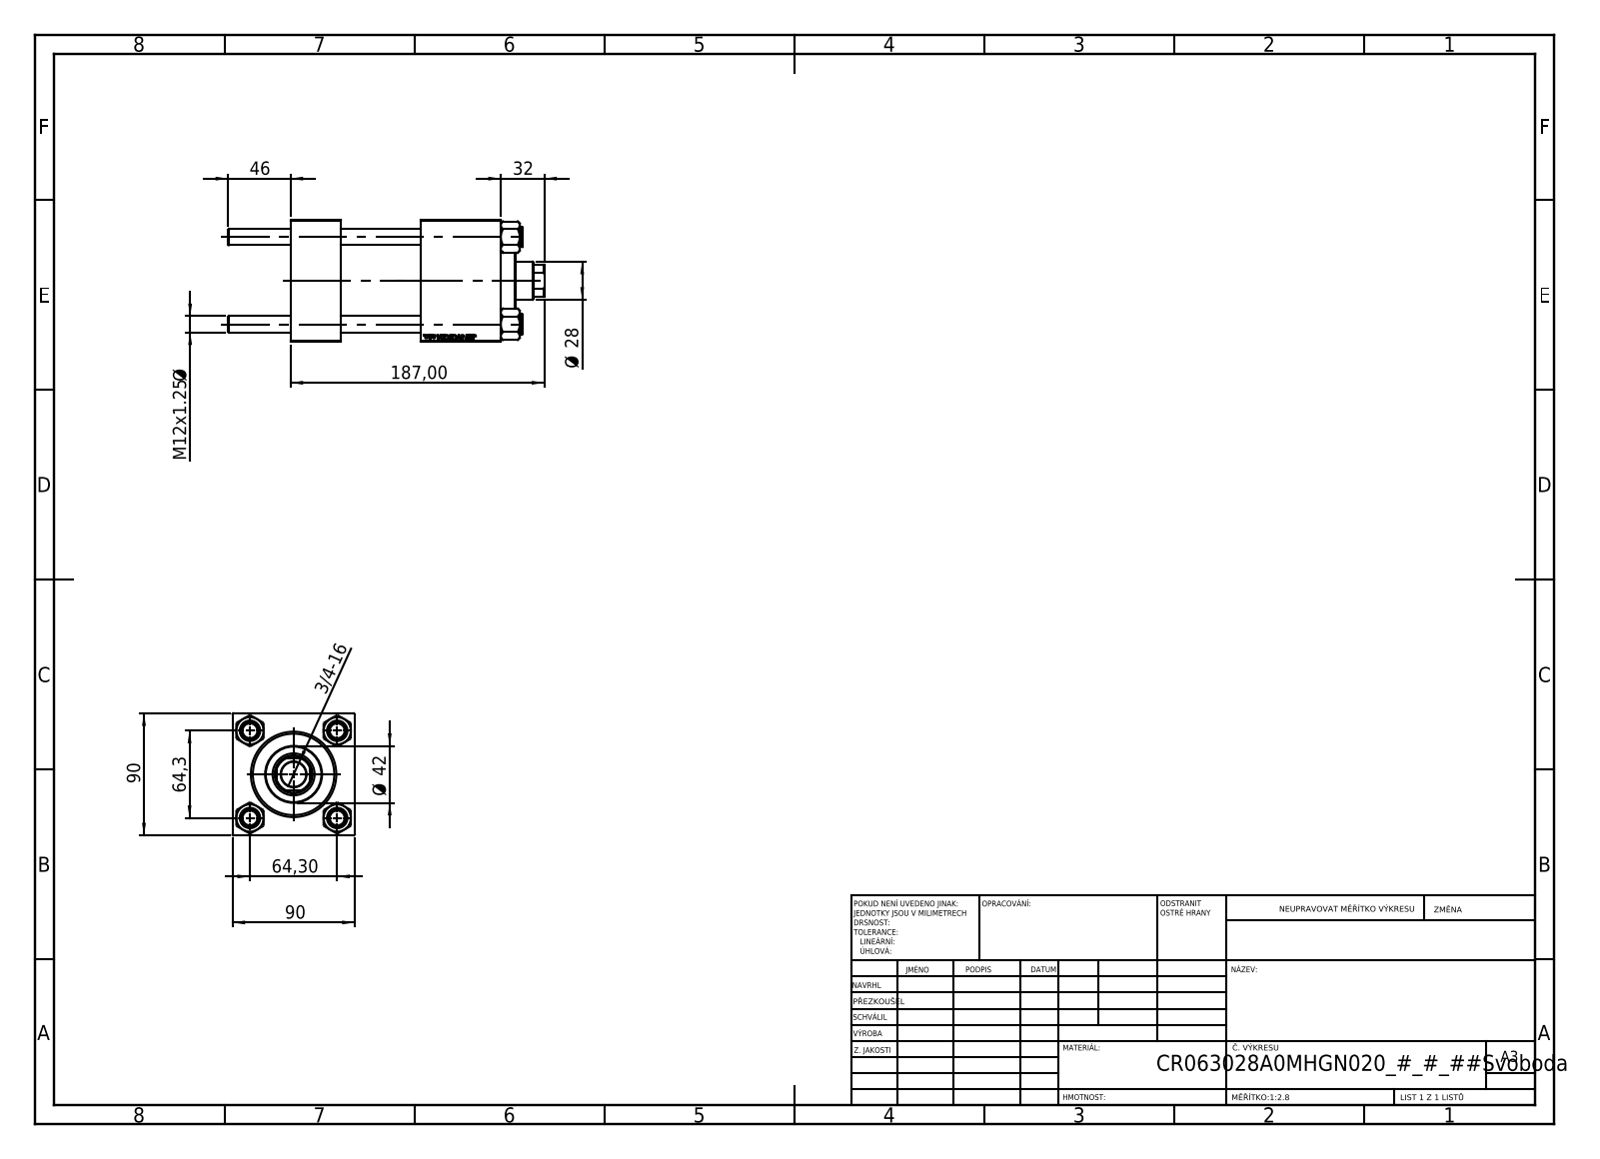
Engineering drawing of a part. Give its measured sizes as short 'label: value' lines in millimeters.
name: V215_VC_A; CR025_012_A_0_G_A_G_M_020_+#_##_TYCINKA; NUT_M5; V215CR_BODY_A (+1 more)
written by: SolidWorks 2019 (CONFIG_CONTROL_DESIGN)
unit: mm
bodies: 11 solids, 1134 faces (520 planar, 78 cylindrical, 536 other)
size: 233 × 90 × 90
volume: 981 287 mm³; area: 195 264 mm²
holes: 4× ⌀12, 2× ⌀7, 2× ⌀20.96, 2× ⌀30, 1× ⌀18.5, 1× ⌀28, 1× ⌀31, 1× ⌀50, 1× ⌀60, 1× ⌀63
bosses: 4× ⌀15, 1× ⌀69, 1× ⌀42
rounds: 1× R13.5
face distances: 90, 59, 37, 155, 118, 96, 126.3, 89.3, 30.3, 28.7
hole spacings: 45.47, 64.3, 90.93, 97.5
